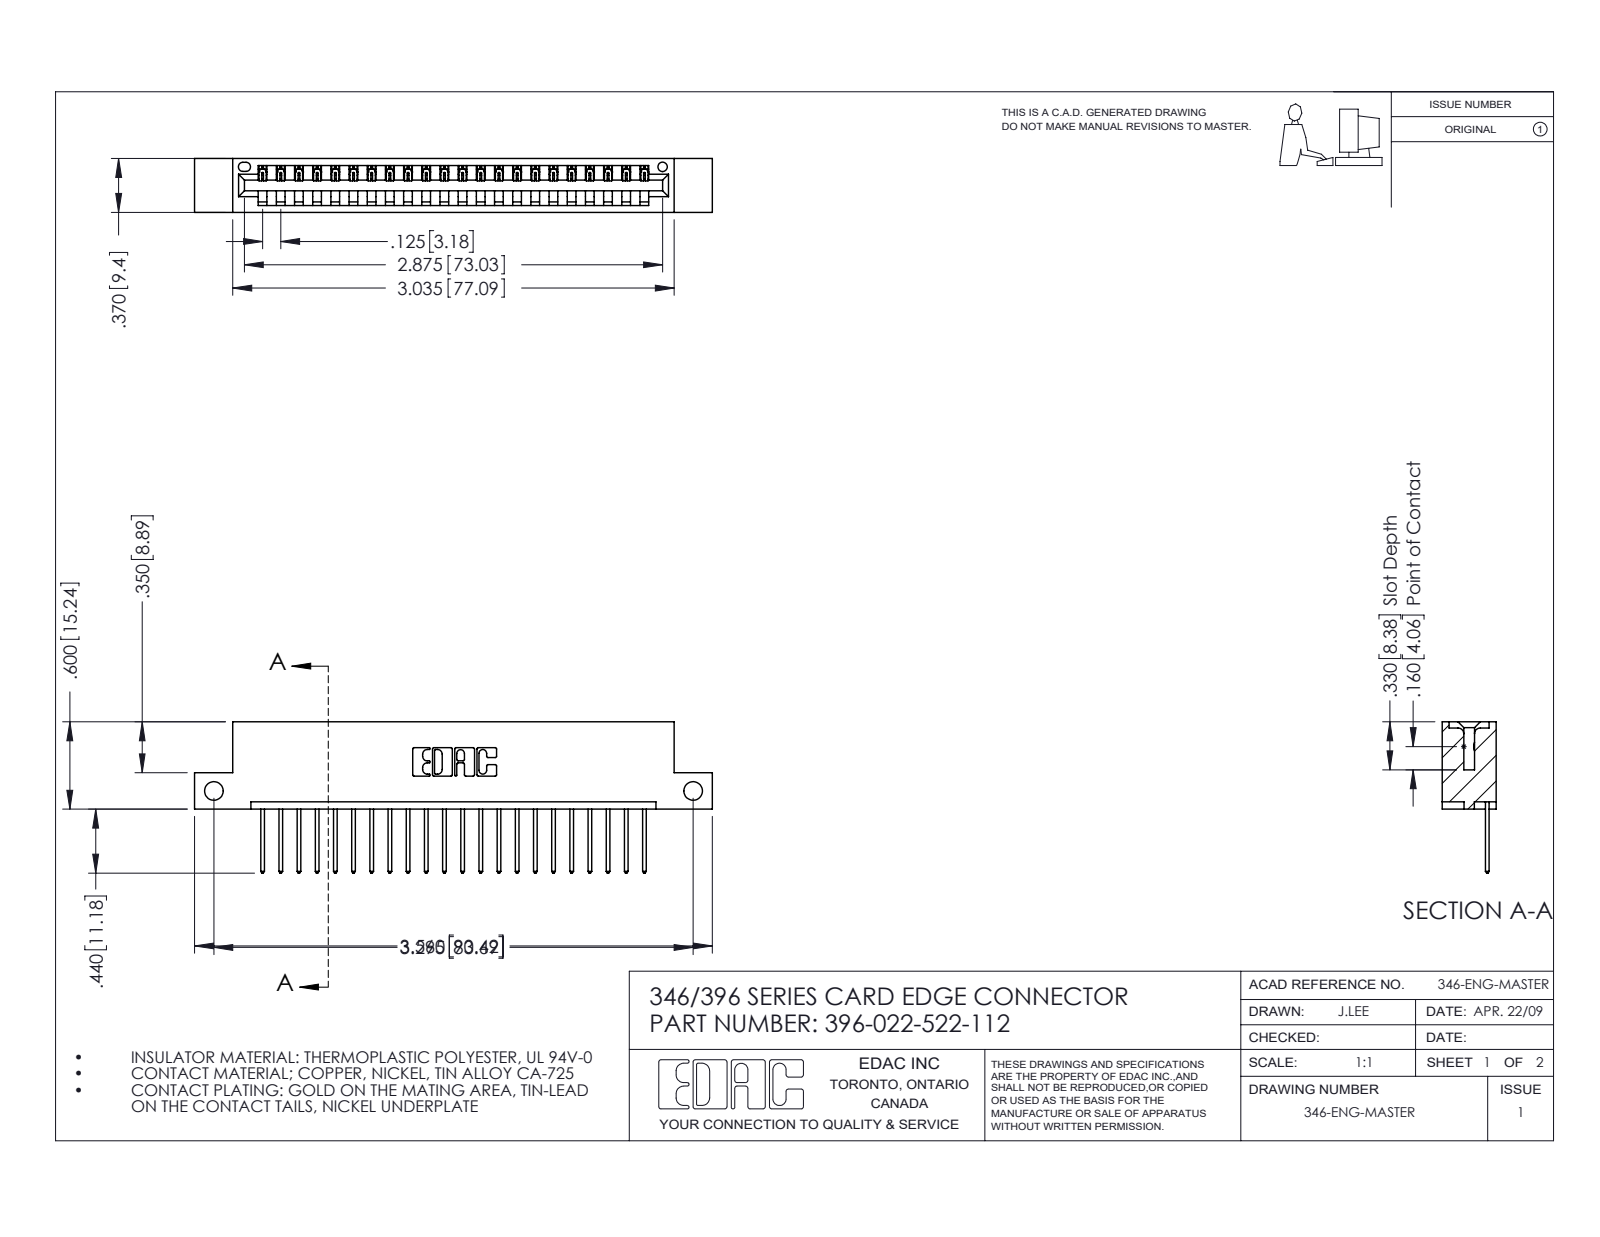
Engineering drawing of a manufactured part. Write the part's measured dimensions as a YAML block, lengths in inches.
part_name: "345-292-001_345-293-122; 396-022-522-112; 346 Part_Flush Mounting Lugs - Side Mount"
step_written_by: "SolidWorks 2016 (CONFIG_CONTROL_DESIGN)"
units: inches
bodies: {solids: 23, faces: 1398, planar: 956, cylindrical: 442, other: 0}
overall_size: [3.56, 1.04, 0.37]
volume: 0.515
surface_area: 15.9
round_holes:
  - {diameter: 0.128, count: 2}
  - {diameter: 0.064, count: 1}
partial_cylinders:
  - {radius: 0.006, count: 44}
  - {radius: 0.01, count: 44}
  - {radius: 0.01, count: 22}
  - {radius: 0.007, count: 6}
  - {radius: 0.031, count: 6}
  - {radius: 0.026, count: 3}
  - {radius: 0.031, count: 2}
  - {radius: 0.04, count: 2}
face_to_face_distances: [0.048, 0.322, 0.25, 0.37, 0.072, 0.298, 0.025, 0.148, 0.222, 0.1]
hole_center_spacings: [3.295]
